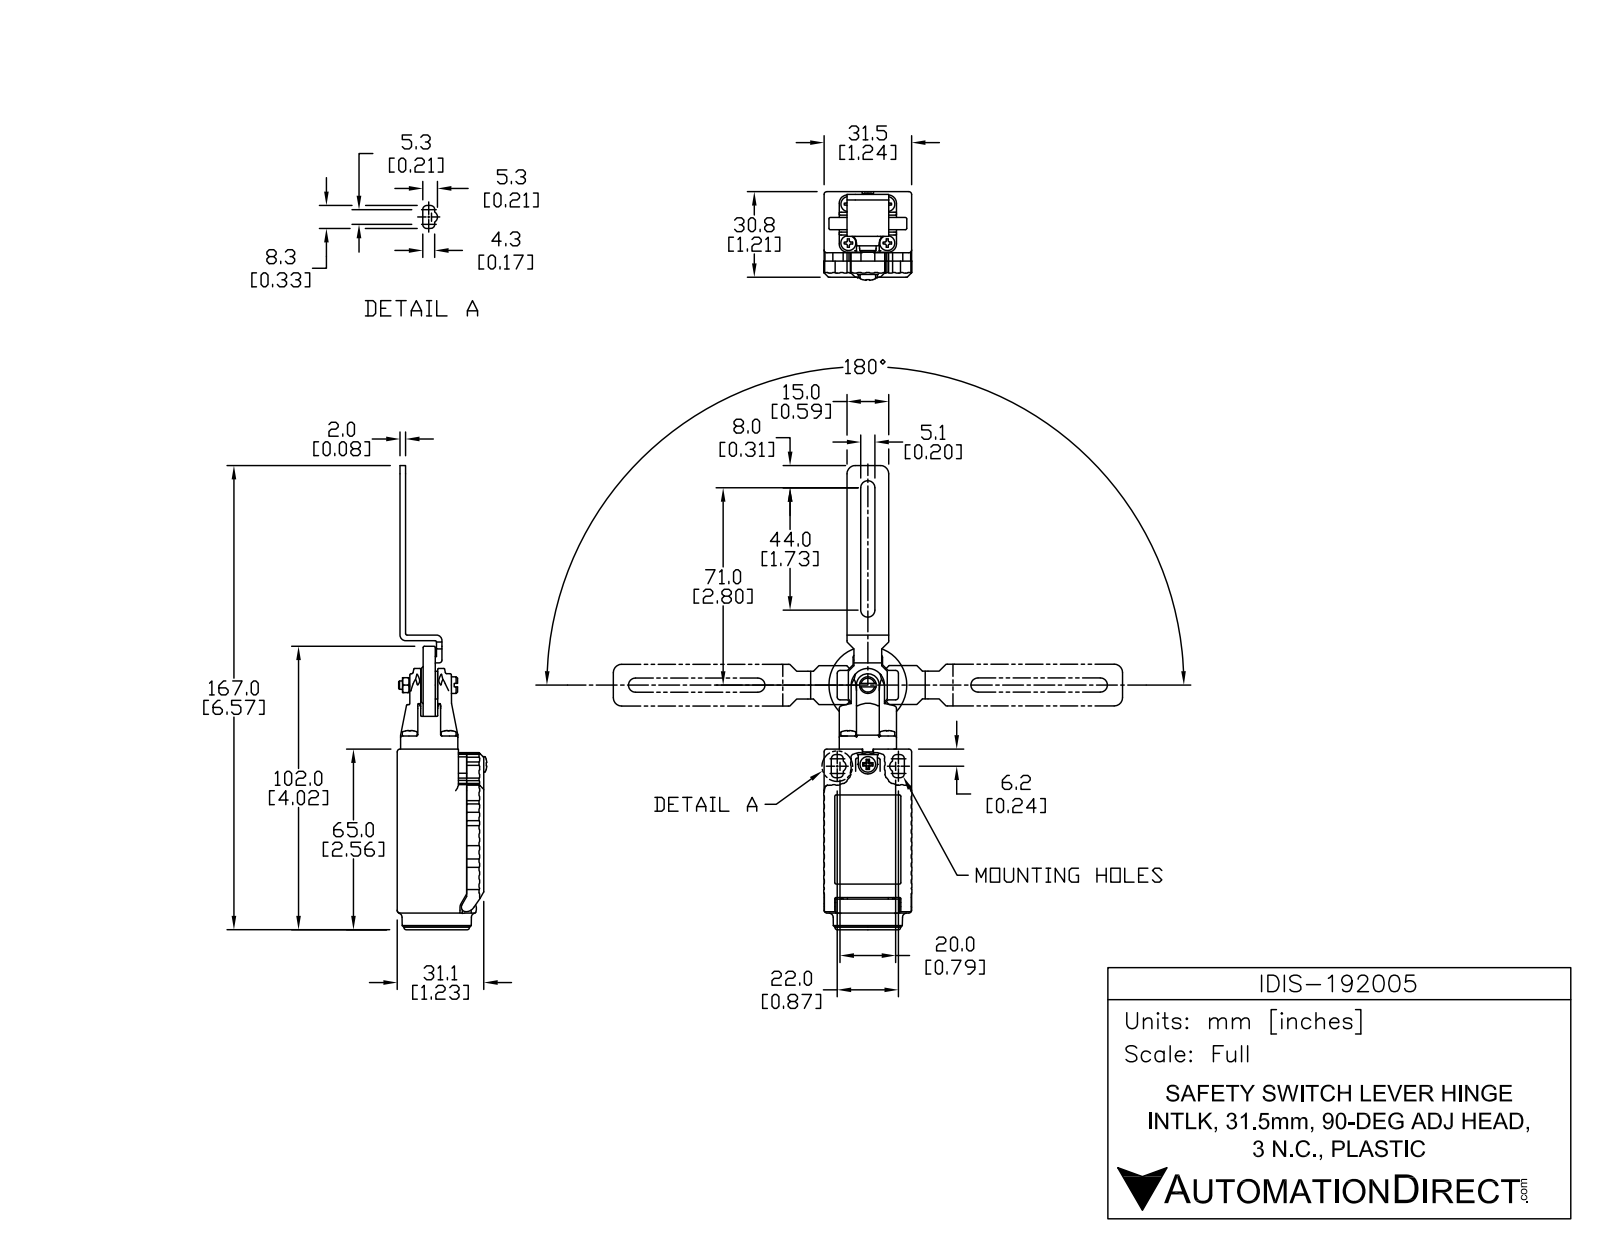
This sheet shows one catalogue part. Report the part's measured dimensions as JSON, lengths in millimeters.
{"part_name": "IDIS-192005", "step_written_by": "SolidWorks 2013 (AUTOMOTIVE_DESIGN)", "units": "millimeters", "bodies": {"solids": 1, "faces": 668, "planar": 270, "cylindrical": 240, "other": 158}, "overall_size": [176.7, 32.2, 31.5], "volume_mm3": 67552, "surface_area_mm2": 21014, "round_holes": [[4, 2], [3, 1], [16.19, 1], [18.5, 1], [21.2, 1]], "round_bosses_or_shafts": [[5.4, 4], [28, 1], [25, 1], [23, 1], [17.19, 1], [13.4, 1], [10, 1], [6, 1]], "partial_cylinders_radius": [[0.5, 71], [0.25, 32], [1, 11], [0.12, 9], [1.5, 8], [2.4, 6], [3, 6], [2, 4]], "face_to_face_distances": [31.5, 5.6, 0.5, 9.3, 1.9, 3.2, 2.8, 30.2, 20.9, 19], "hole_center_spacings": [22, 88.58, 88.59]}
